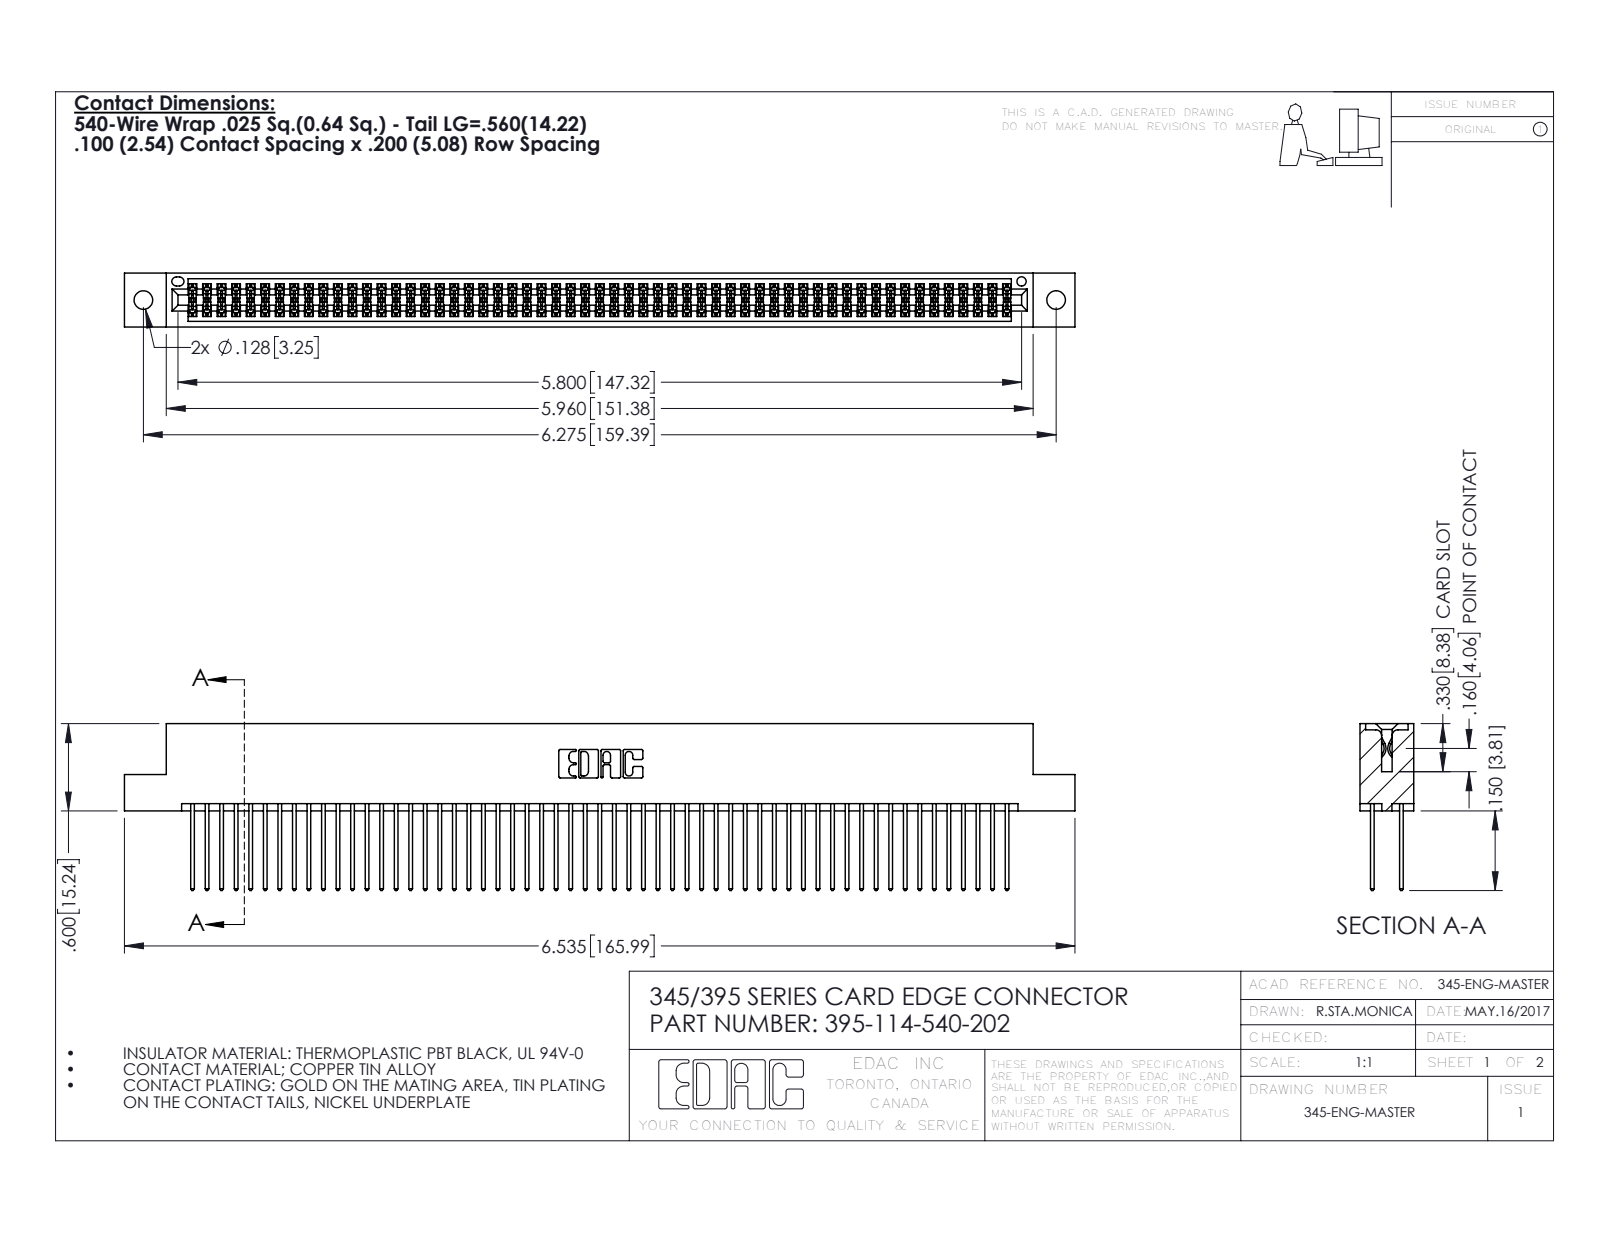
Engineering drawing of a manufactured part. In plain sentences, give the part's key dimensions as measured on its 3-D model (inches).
The part is named "395-114-540-202; 345 Part_Flush Mounting Lugs - 0.128 Dia; 345-292-001_345-293-140". Its 3-D file was written by "SolidWorks 2016 (CONFIG_CONTROL_DESIGN)". It is 115 solids with 5826 faces: 3842 planar, 1984 cylindrical and 0 other. Overall it measures 6.535 by 1.147 by 0.37 inches. Its volume is 1.017 cubic inches and its surface area 41.3 square inches. Round holes: 2 of diameter 0.128, 1 of diameter 0.064. Partial cylindrical surfaces (rounded edges, fillets, slot ends): 171 of radius 0.006, 114 of radius 0.01, 22 of radius 0.01, 6 of radius 0.007, 6 of radius 0.031, 3 of radius 0.026, 2 of radius 0.014, 2 of radius 0.019. The main face-to-face distances are 0.298, 0.072, 0.2, 0.098, 0.272, 0.025, 0.37, 0.225, 0.175, 0.149. The hole center spacings are 0.27, 6.039, 6.275.
